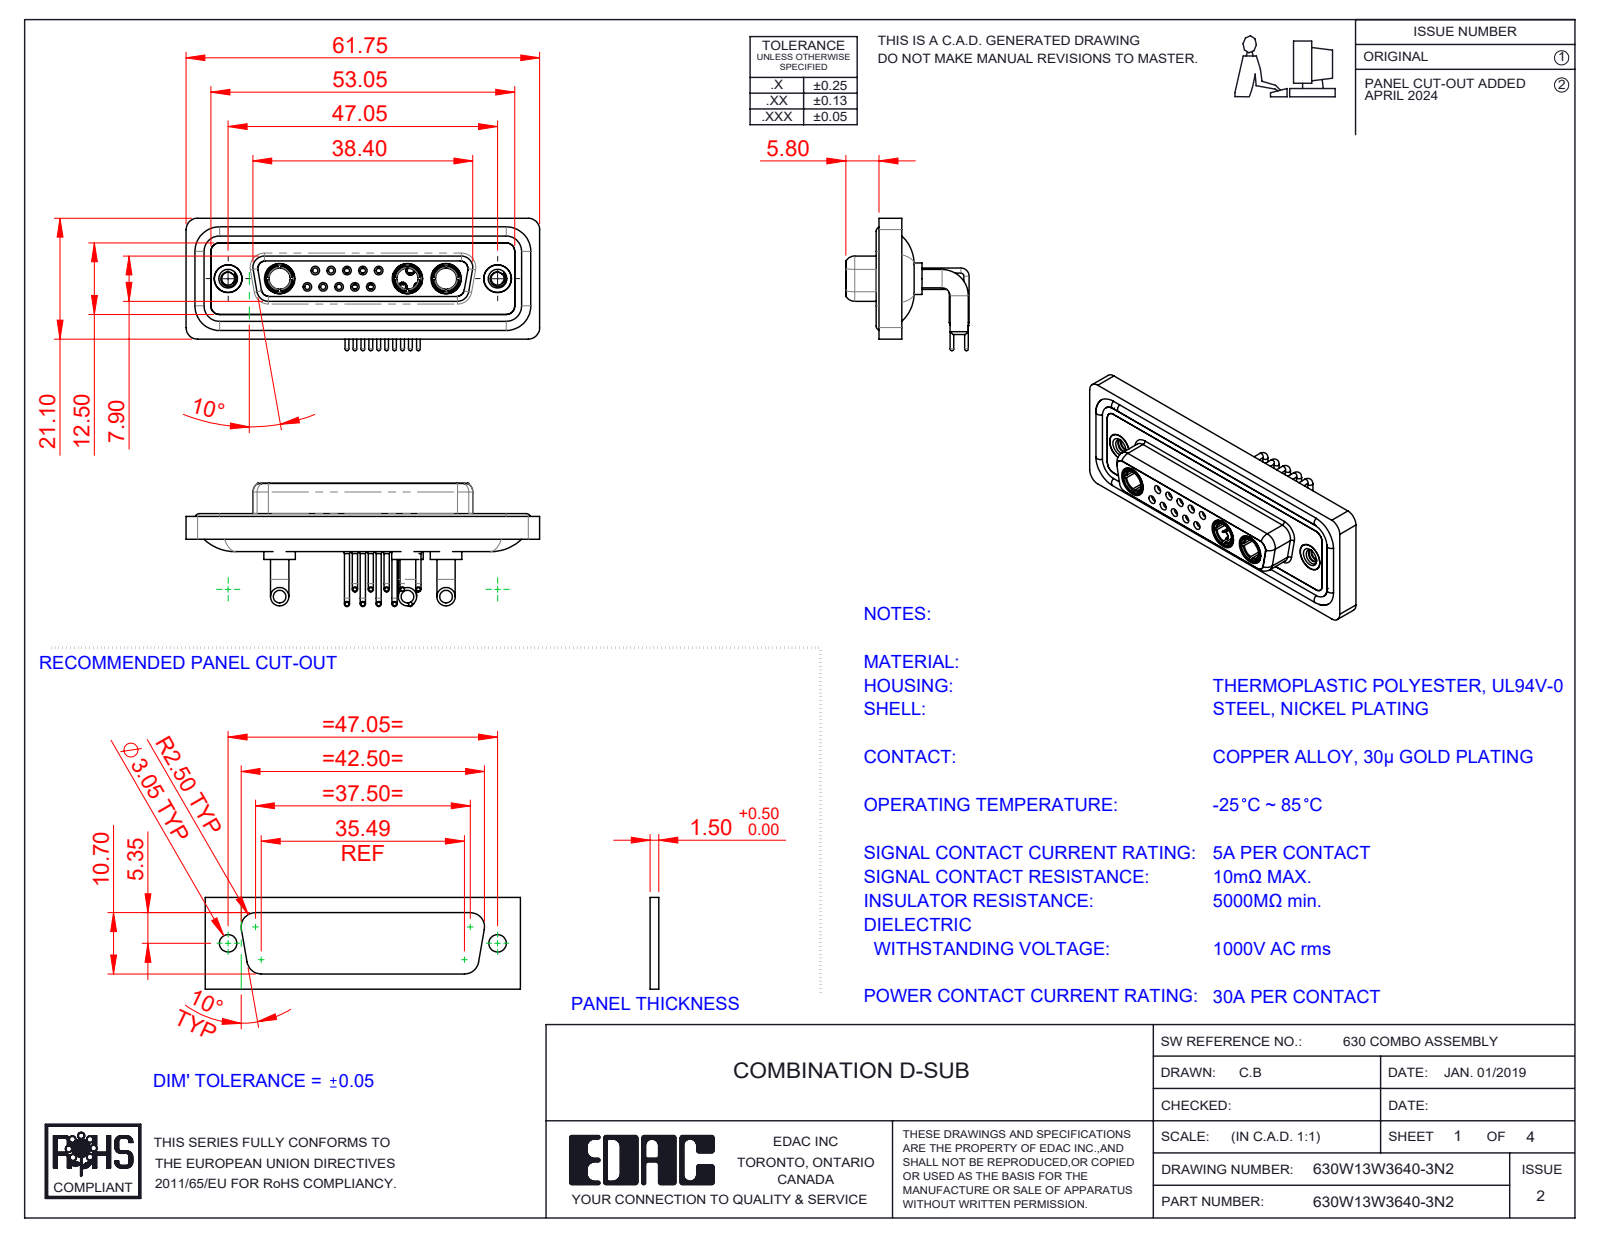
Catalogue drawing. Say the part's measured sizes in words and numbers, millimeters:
The part is named "630Combo Shell Rear_25 Contacts; 630Combo Shell Front_25 Contacts; 630Combo Threaded Rivet_2; Power Socket_30A RA (+5 more)". Its 3-D file was written by "SolidWorks 2023 (CONFIG_CONTROL_DESIGN)". It is 23 solids with 1150 faces: 342 planar, 493 cylindrical and 315 other. Overall it measures 61.75 by 23.12 by 21.53 millimeters. Its volume is 8 554 cubic millimeters and its surface area 14 351 square millimeters. Round holes: 10 of diameter 0.9, 10 of diameter 1.1, 10 of diameter 1.5, 10 of diameter 2, 5 of diameter 1.6, 5 of diameter 1.7, 5 of diameter 4.85, 3 of diameter 3.7, 3 of diameter 5.3, 2 of diameter 2.26, 2 of diameter 4, 2 of diameter 4.05. Round bosses or shafts: 15 of diameter 0.9, 12 of diameter 1.6, 10 of diameter 0.65, 6 of diameter 3.2, 5 of diameter 2, 5 of diameter 1.5, 3 of diameter 5.5, 3 of diameter 5.2. Partial cylindrical surfaces (rounded edges, fillets, slot ends): 18 of radius 1.5, 18 of radius 2, 8 of radius 1.35, 8 of radius 1.6, 4 of radius 0.25, 4 of radius 0.5, 4 of radius 0.6, 4 of radius 0.65. The main face-to-face distances are 0.4, 1.8, 4.1, 1.1, 1.6, 3.1, 2.5, 1.5, 3.7, 1.4. The hole center spacings are 3.16, 2.77, 5.54, 5.04, 8.31, 5.03, 7.49, 11.08.
